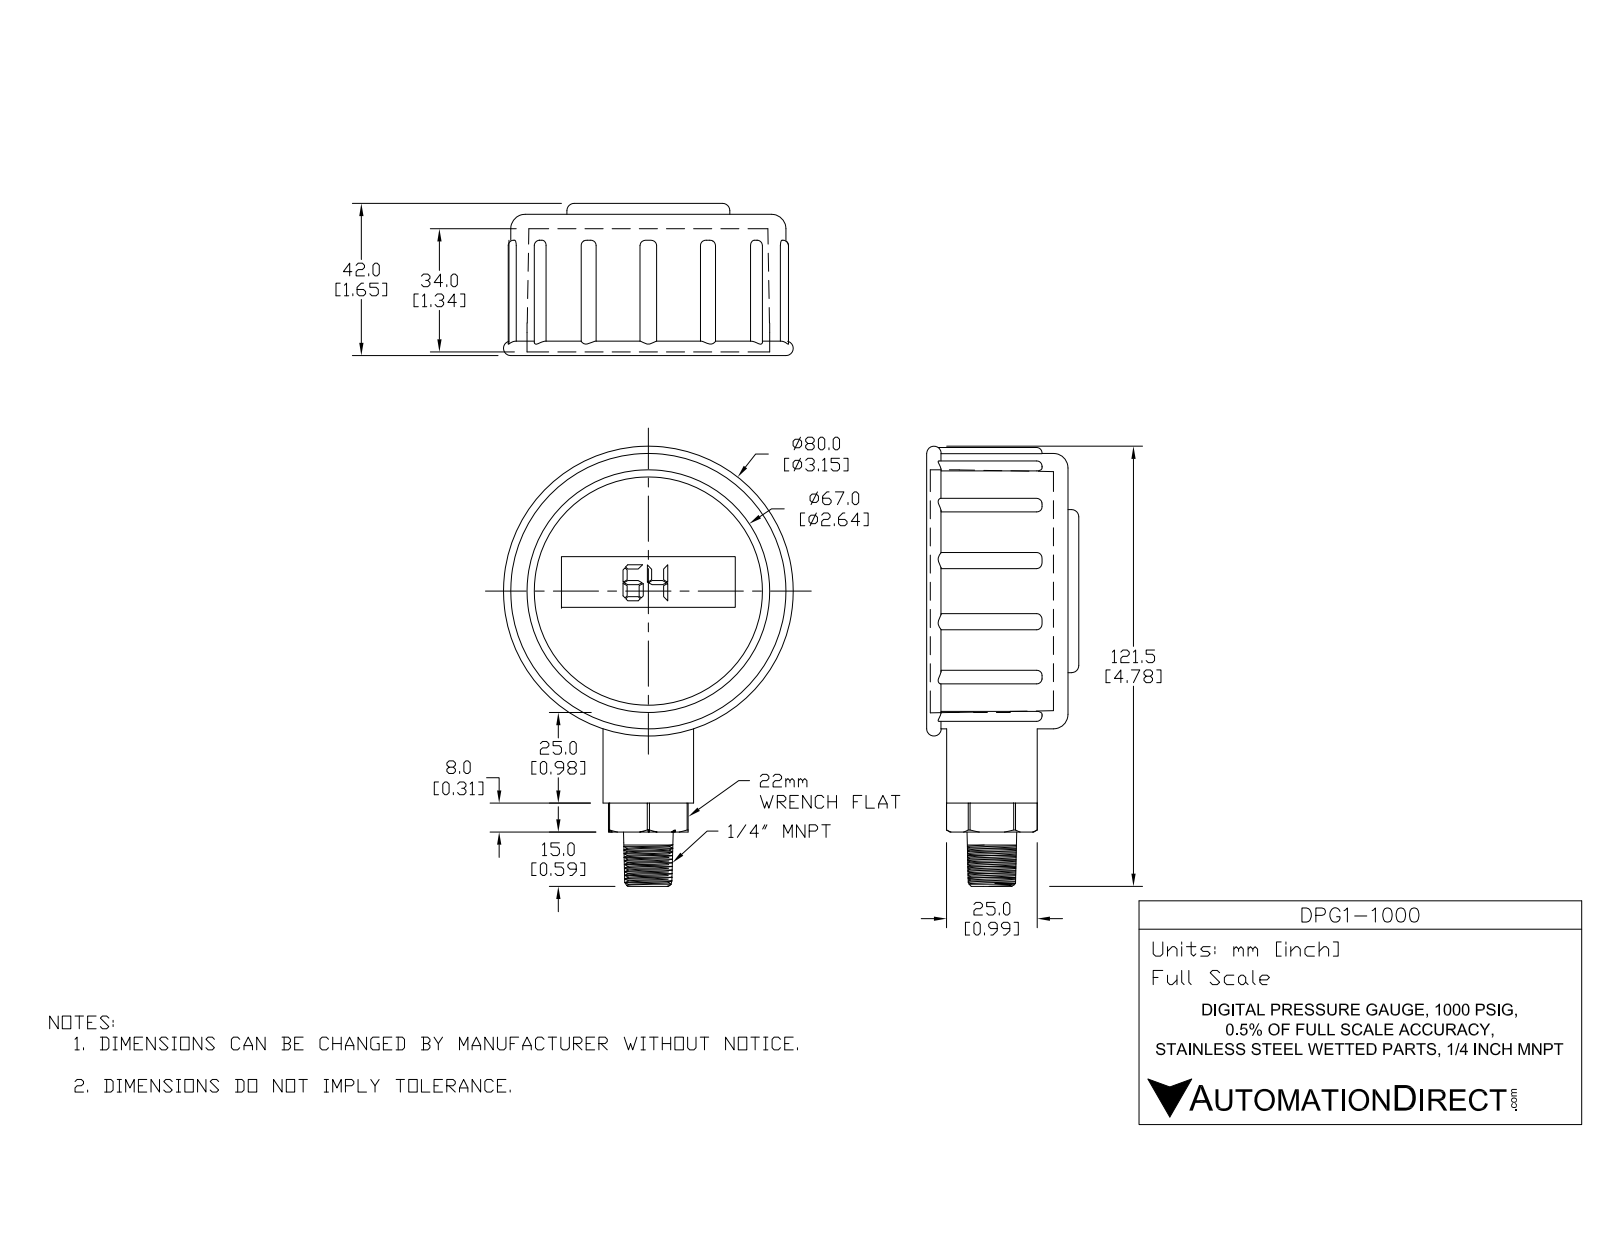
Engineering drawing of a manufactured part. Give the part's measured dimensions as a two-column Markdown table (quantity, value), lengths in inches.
| quantity | value |
| --- | --- |
| part name | DPG1-1000 |
| STEP written by | SolidWorks 2021 (CONFIG_CONTROL_DESIGN) |
| units | inches |
| bodies | 4 solids, 181 faces (71 planar, 49 cylindrical, 61 other) |
| overall size | 4.788 × 3.15 × 1.654 |
| volume | 11.97 in³ |
| surface area | 71.27 in² |
| round holes (diameter × count) | 2.48 × 1, 2.645 × 1 |
| round bosses / shafts (diameter × count) | 2.992 × 1, 2.638 × 1, 1.772 × 1, 0.984 × 1, 0.394 × 1 |
| partial cylindrical surfaces (radius × count) | 0.094 × 13, 0.335 × 6, 1.496 × 1 |
| main face-to-face distances | 1.337, 0.157, 1.494, 0.118, 0.276, 1.612, 1.654, 1.535, 1.378, 0.041 |
